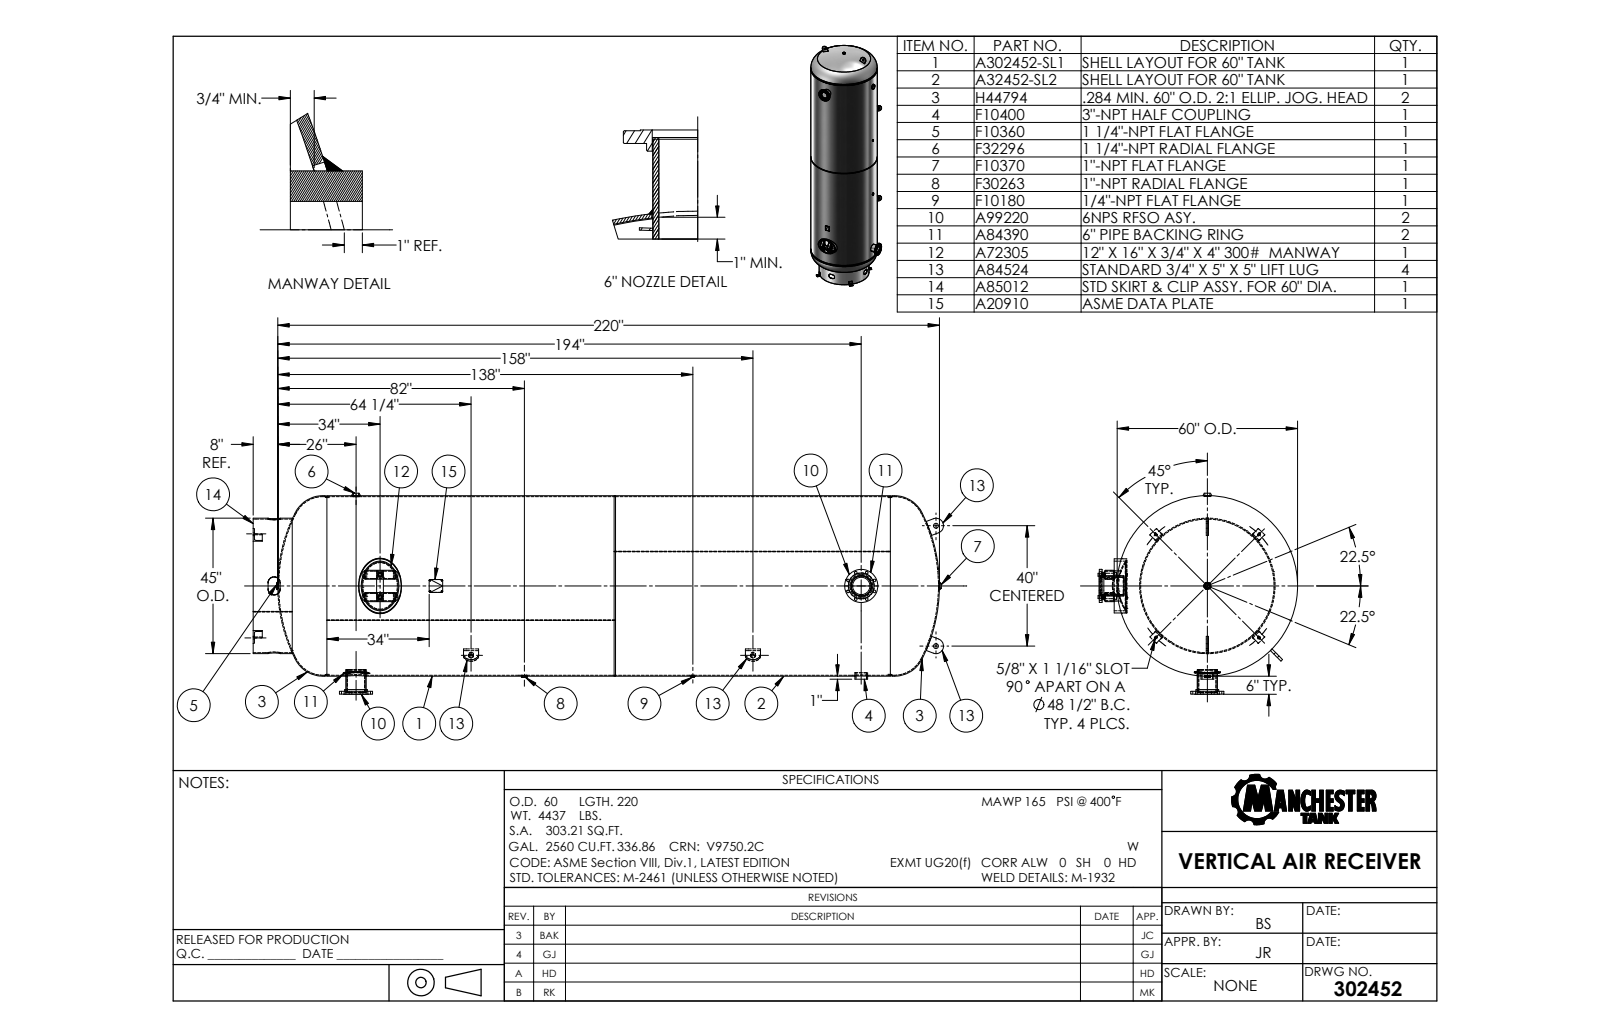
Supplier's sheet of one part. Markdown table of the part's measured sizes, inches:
| quantity | value |
| --- | --- |
| part name | 302452 |
| STEP written by | SolidWorks 2011 (CONFIG_CONTROL_DESIGN) |
| units | inches |
| bodies | 0 solids, 363 faces (129 planar, 153 cylindrical, 81 other) |
| overall size | 229.51 × 66.8 × 66.371 |
| round holes (diameter × count) | 0.875 × 16, 1.625 × 2, 1.625 × 2, 1.66 × 2, 5.761 × 2, 6.72 × 2, 0.54 × 1, 1.315 × 1, 1.315 × 1, 3.5 × 1, 44.376 × 1, 58.5 × 1 |
| round bosses / shafts (diameter × count) | 11 × 2, 8.5 × 2, 6.625 × 2, 2.375 × 2, 1 × 2, 60 × 1, 45 × 1, 4.25 × 1 |
| partial cylindrical surfaces (radius × count) | 0.255 × 8, 0.312 × 4, 0.313 × 4, 0.375 × 4, 0.562 × 4, 1.318 × 4, 2.5 × 4, 5.917 × 1 |
| main face-to-face distances | 24.356, 96, 120.356, 91.625, 187.625, 211.981, 0.063, 0.75, 0.75, 4.937 |
| hole center spacings | 6.718, 3.635, 4.75, 8.777, 4.75, 4.75, 3.636, 8.777 |
